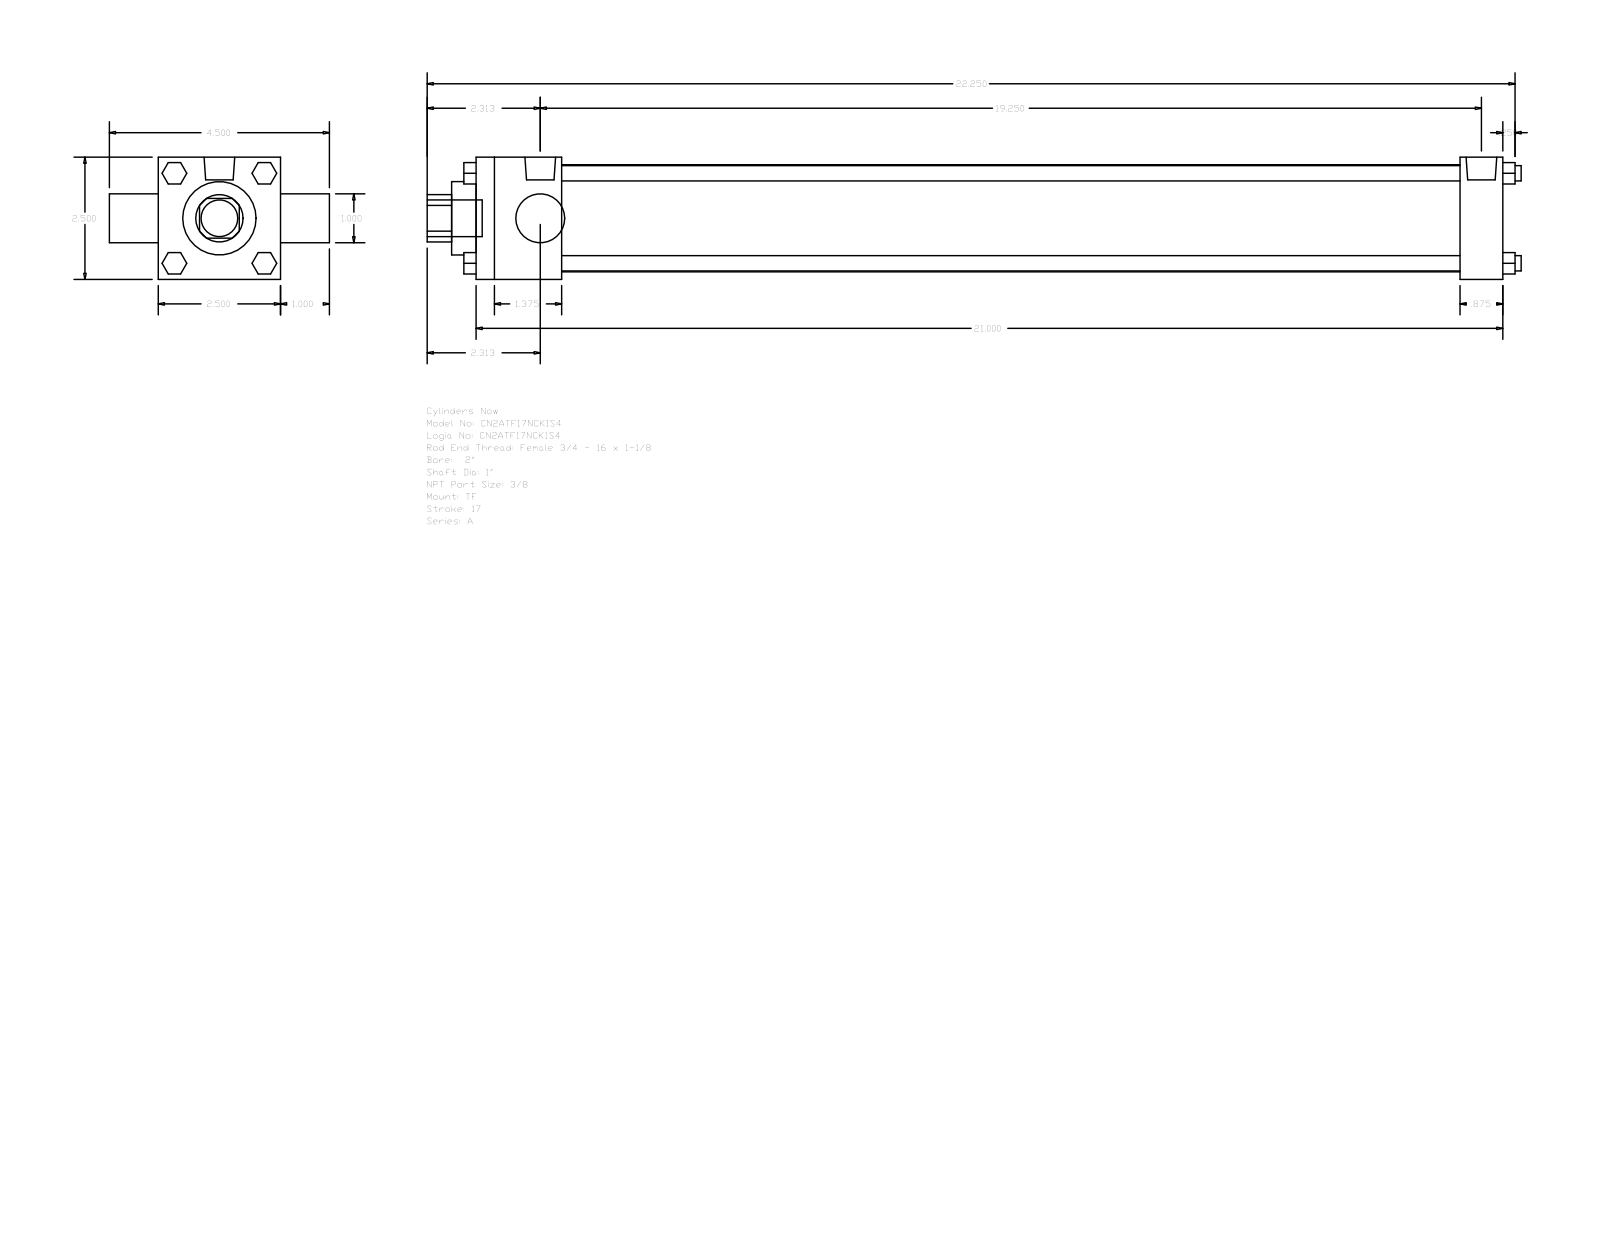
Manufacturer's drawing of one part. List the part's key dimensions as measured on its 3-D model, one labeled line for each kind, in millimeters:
Part name (STEP PRODUCT): A_TF__0200_1
STEP written by: GSSL Pune (CONFIG_CONTROL_DESIGN)
Units: millimetres
Bodies: 0 solids, 120 faces (92 planar, 28 cylindrical, 0 other)
Overall size (bounding box): 568.33 × 114.3 × 63.5
Round holes (diameter × count): ⌀25.4 ×2, ⌀38.1 ×1, ⌀55.63 ×1
Round bosses / shafts (diameter × count): ⌀7.94 ×4, ⌀5.56 ×3, ⌀15.93 ×2, ⌀19.05 ×1
Partial cylindrical surfaces — rounded edges, fillets, slot ends (radius × count): R12.29 ×1
Main face-to-face distances: 63.5, 533.4, 44.45, 511.18, 466.73, 488.95, 22.22, 25.4, 88.9, 546.1
